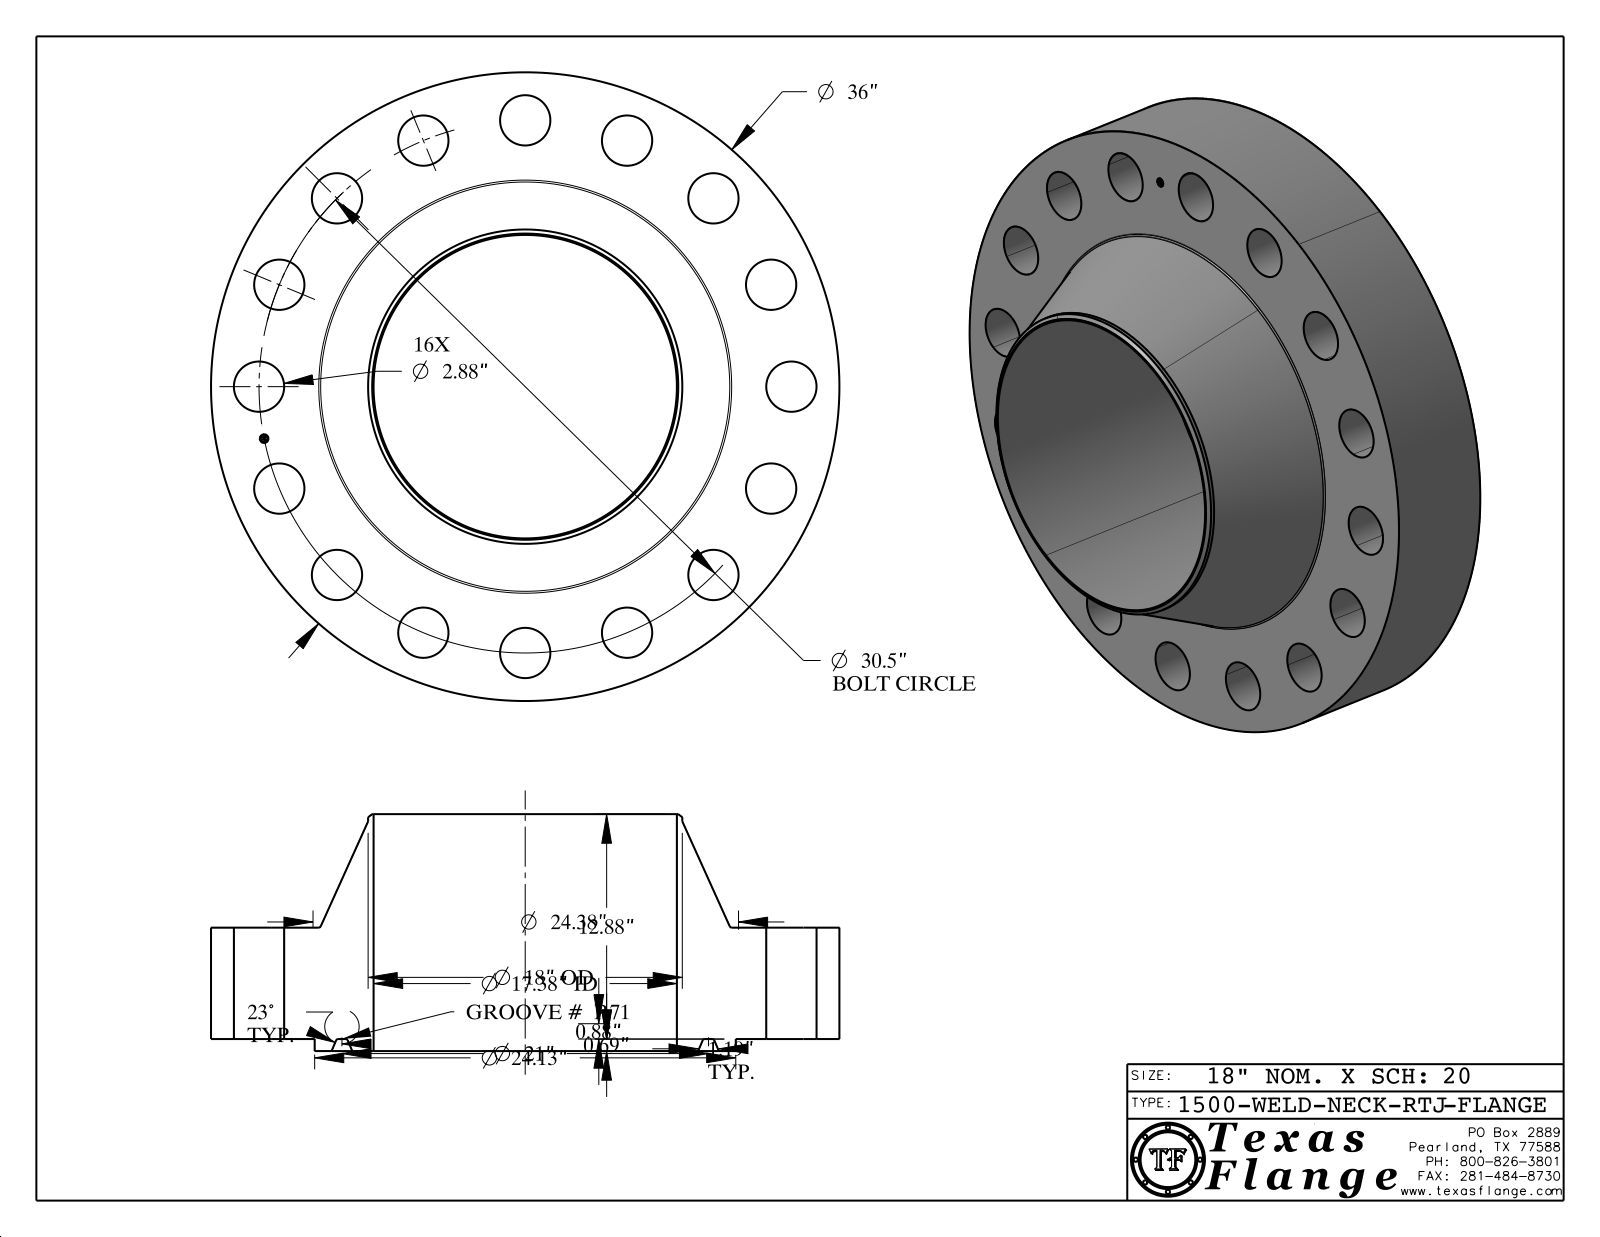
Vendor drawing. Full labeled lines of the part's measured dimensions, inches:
Part name (STEP PRODUCT): 1500-WELD-NECK-RTJ
STEP written by: CATIA V5 STEP AP214 (AUTOMOTIVE_DESIGN)
Units: inches
Bodies: 1 solid, 445 faces (371 planar, 60 cylindrical, 14 other)
Overall size (bounding box): 36 × 36 × 13.568
Volume: 5 060 in³ · Surface area: 4 121 in²
Round holes (diameter × count): ⌀2.88 ×16, ⌀0.495 ×1, ⌀17.376 ×1
Round bosses / shafts (diameter × count): ⌀0.03 ×8, ⌀36 ×1, ⌀24.125 ×1, ⌀18 ×1, ⌀0.39 ×1
Main face-to-face distances: 6.38, 0.688, 7.068, 13.568, 12.88, 6.5, 7.053, 6.365, 0.015, 6.515
Hole centre spacings: 5.95, 16.945, 29.914, 15.25, 11.672, 11.672, 15.25, 21.567
